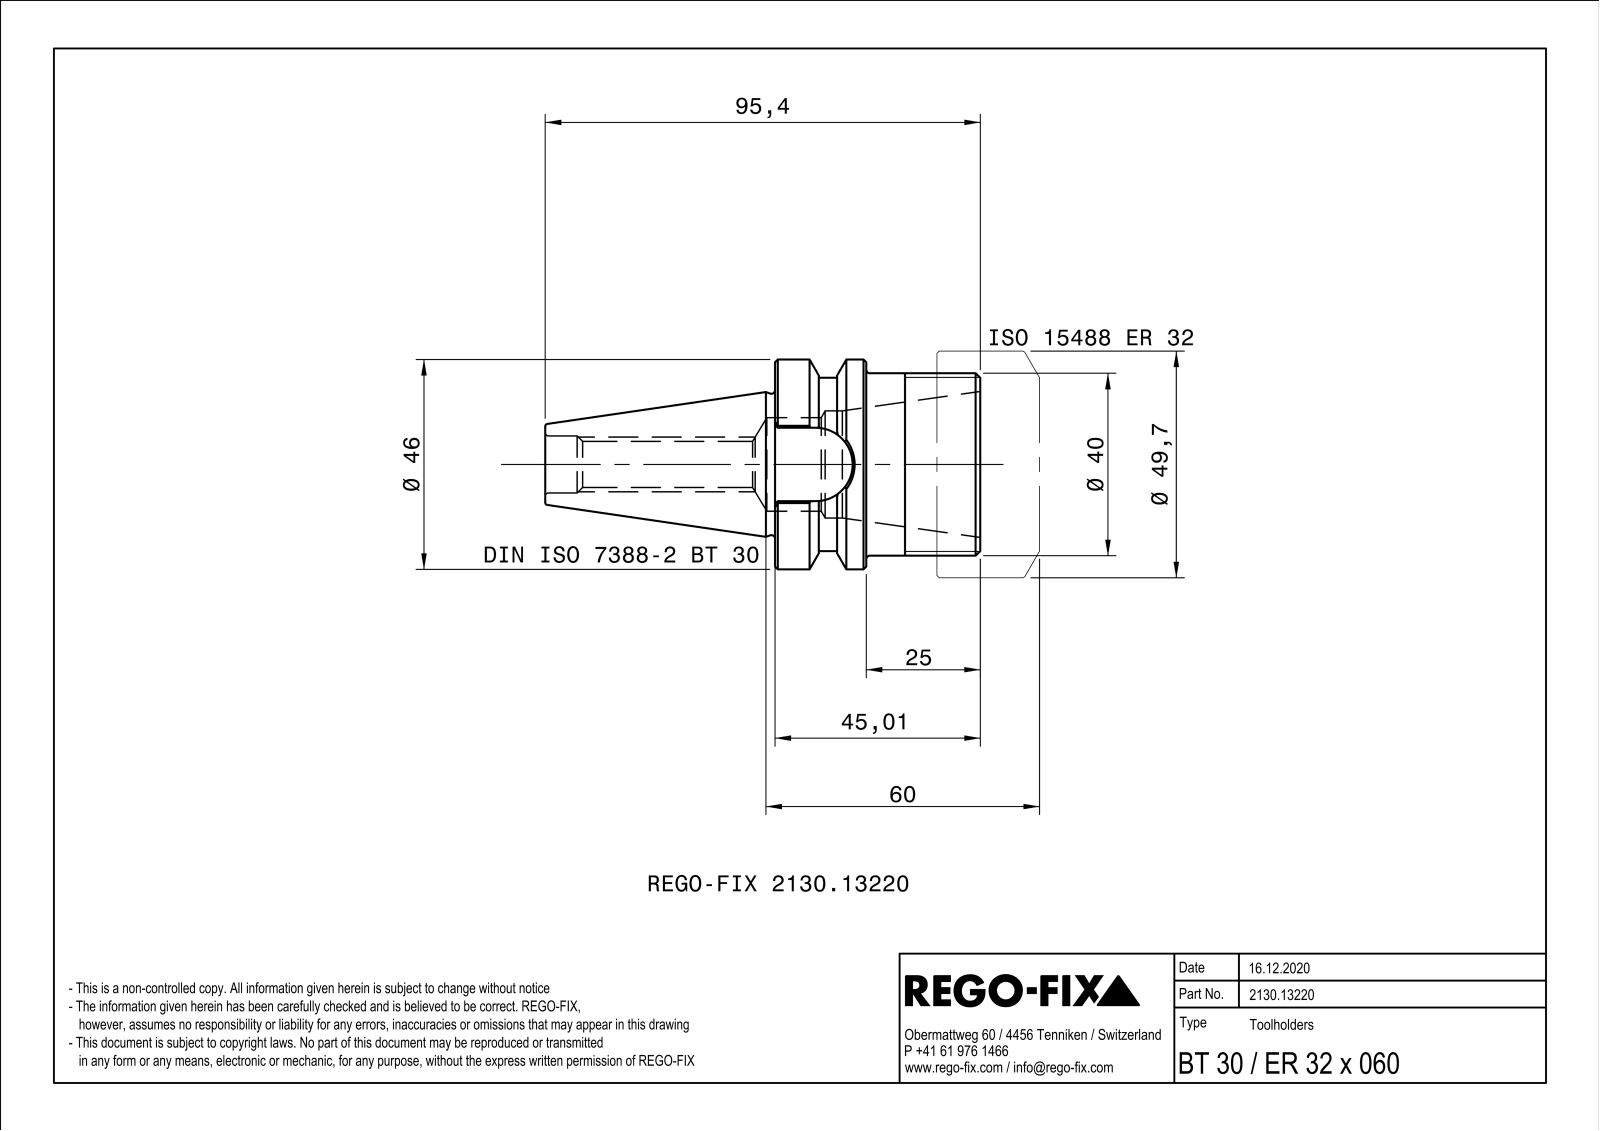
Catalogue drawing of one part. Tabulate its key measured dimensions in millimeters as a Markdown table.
| quantity | value |
| --- | --- |
| part name | NOCUT |
| STEP written by | SIEMENS PLM Software Solid Edge ST10 (AUTOMOTIVE_DESIGN) |
| units | millimeters |
| bodies | 2 solids, 169 faces (62 planar, 45 cylindrical, 62 other) |
| overall size | 95.8 × 46.3 × 46.3 |
| volume | 113 374 mm³ |
| surface area | 35 750 mm² |
| round holes (diameter × count) | 10.11 × 1, 12.2 × 1, 12.5 × 1, 20.5 × 1, 23.5 × 1 |
| round bosses / shafts (diameter × count) | 46.3 × 1, 46 × 1, 40.3 × 1, 40 × 1 |
| partial cylindrical surfaces (radius × count) | 0.5 × 8, 8.05 × 1, 19 × 1 |
| main face-to-face distances | 32.5, 25, 45.2, 45, 24.8, 20.2, 25.2, 20, 95.6, 70.6 |
